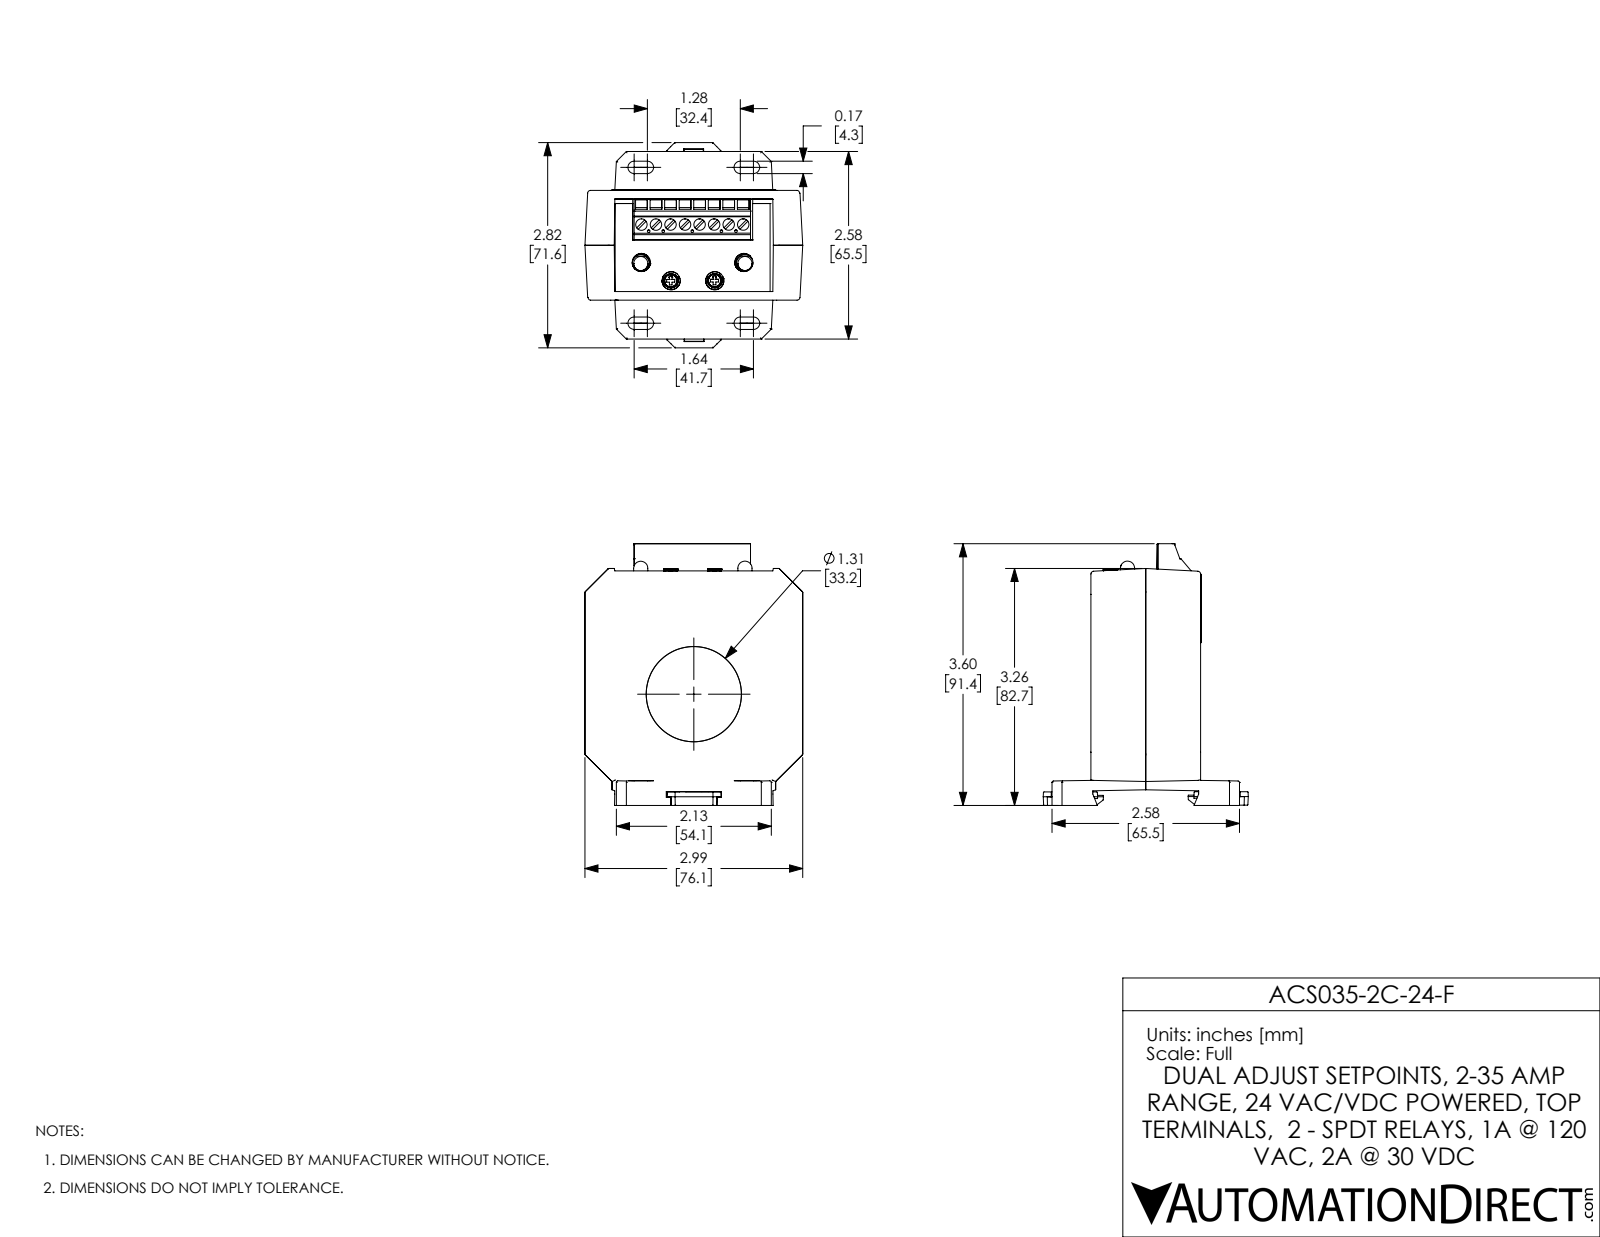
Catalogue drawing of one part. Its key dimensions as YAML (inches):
part_name: "ACS035-2C-24-F"
step_written_by: "SolidWorks 2017 (AUTOMOTIVE_DESIGN)"
units: inches
bodies: {solids: 33, faces: 1584, planar: 980, cylindrical: 426, other: 178}
overall_size: [3.597, 2.995, 2.82]
volume: 4.188
surface_area: 116.9
round_holes:
  - {diameter: 0.25, count: 9}
  - {diameter: 0.03, count: 8}
  - {diameter: 0.036, count: 5}
  - {diameter: 0.05, count: 2}
  - {diameter: 0.185, count: 2}
  - {diameter: 0.125, count: 1}
  - {diameter: 1.663, count: 1}
  - {diameter: 1.821, count: 1}
  - {diameter: 1.979, count: 1}
  - {diameter: 2.138, count: 1}
  - {diameter: 2.296, count: 1}
round_bosses_or_shafts:
  - {diameter: 0.157, count: 8}
  - {diameter: 0.255, count: 2}
  - {diameter: 0.234, count: 2}
  - {diameter: 0.194, count: 2}
  - {diameter: 2.375, count: 1}
  - {diameter: 2.217, count: 1}
  - {diameter: 2.059, count: 1}
  - {diameter: 1.9, count: 1}
partial_cylinders:
  - {radius: 0.004, count: 48}
  - {radius: 0.02, count: 22}
  - {radius: 0.008, count: 18}
  - {radius: 0.012, count: 18}
  - {radius: 0.025, count: 12}
  - {radius: 0.04, count: 9}
  - {radius: 0.008, count: 8}
  - {radius: 0.04, count: 7}
face_to_face_distances: [1.508, 0.079, 1.429, 0.083, 0.063, 2.992, 1.33, 1.35, 0.02, 2.909]
hole_center_spacings: [1.431, 1.431, 0.02, 0.02, 0.42, 0.537, 0.732, 1.04]
